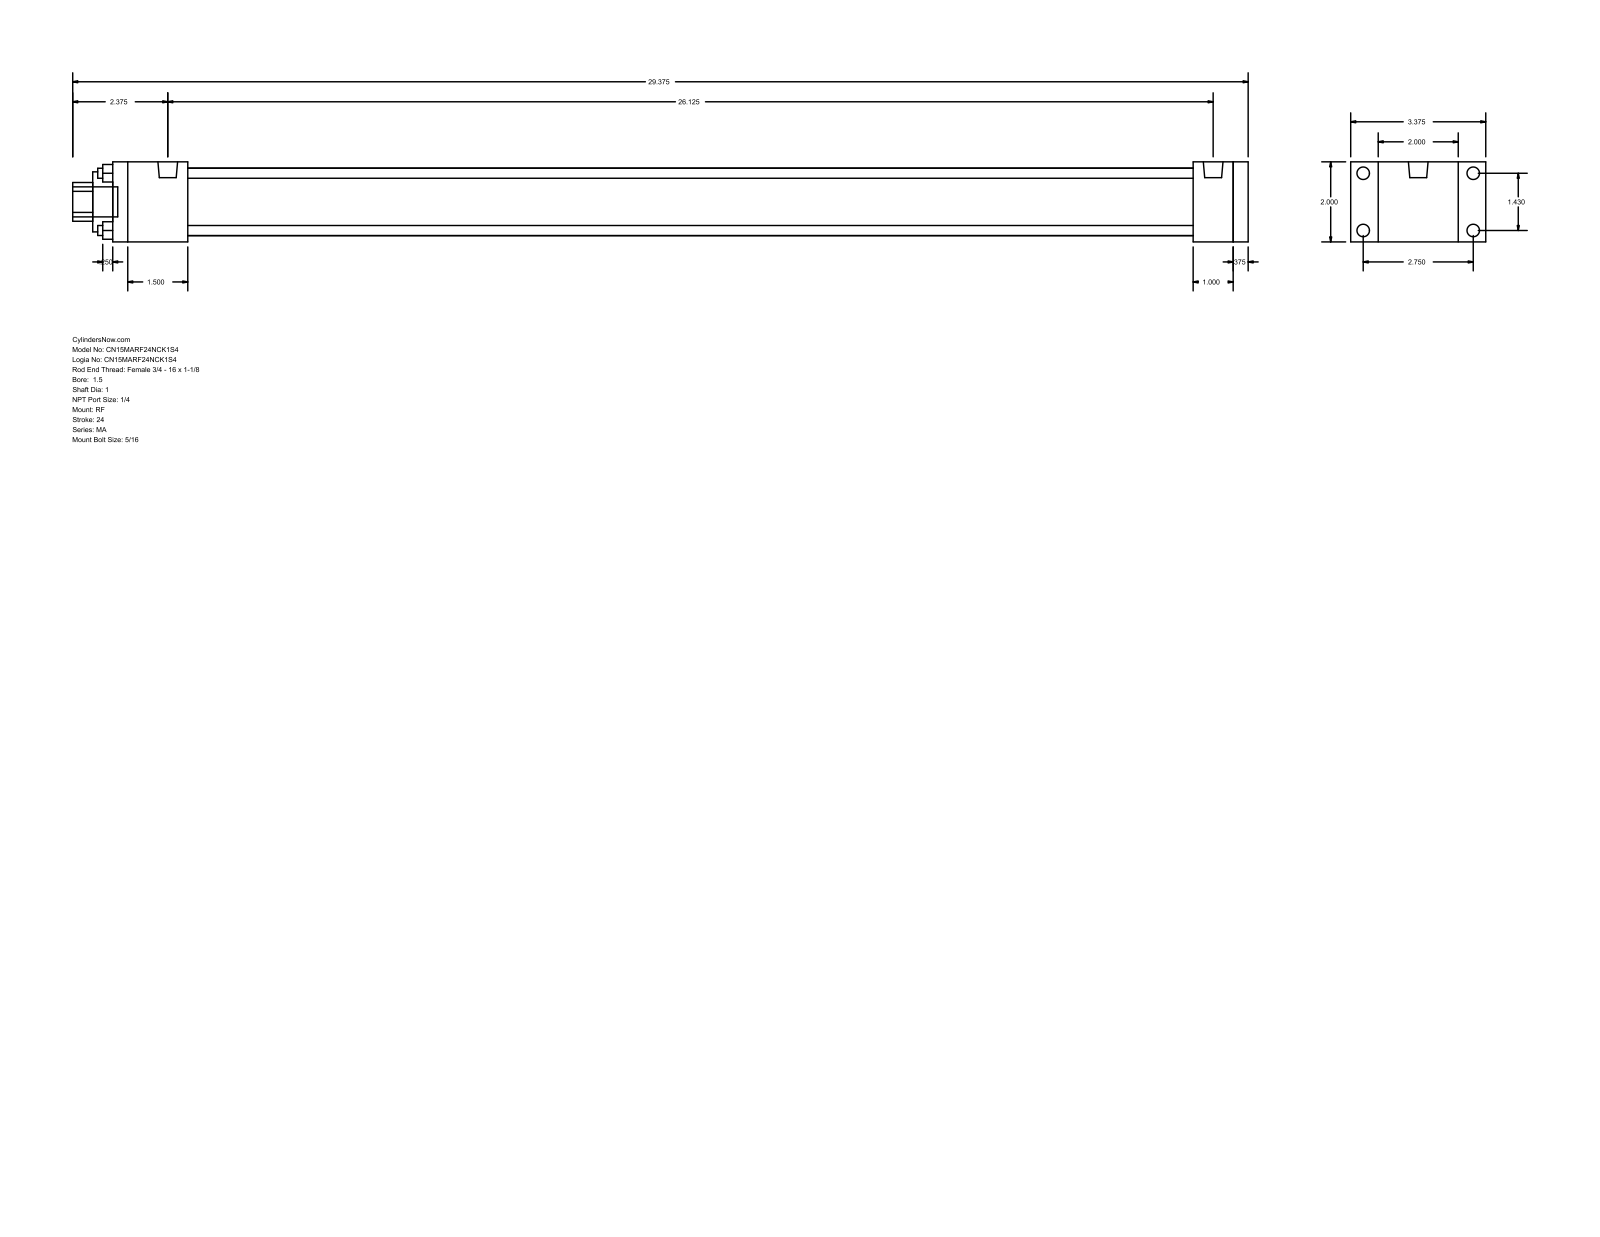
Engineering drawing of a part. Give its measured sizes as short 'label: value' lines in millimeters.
name: MA_RF__0150_1
written by: GSSL Pune (CONFIG_CONTROL_DESIGN)
unit: mm
bodies: 0 solids, 92 faces (64 planar, 28 cylindrical, 0 other)
size: 746.12 × 85.72 × 50.8
holes: 4× ⌀6.35, 1× ⌀25.4, 1× ⌀38.1, 1× ⌀42.93
bosses: 8× ⌀7.94, 2× ⌀12.49, 1× ⌀19.05
rounds: 1× R12.29
face distances: 50.8, 9.52, 720.72, 711.2, 25.4, 685.8, 34.92, 47.63, 638.17, 663.57
hole spacings: 25.68, 36.32, 51.36
